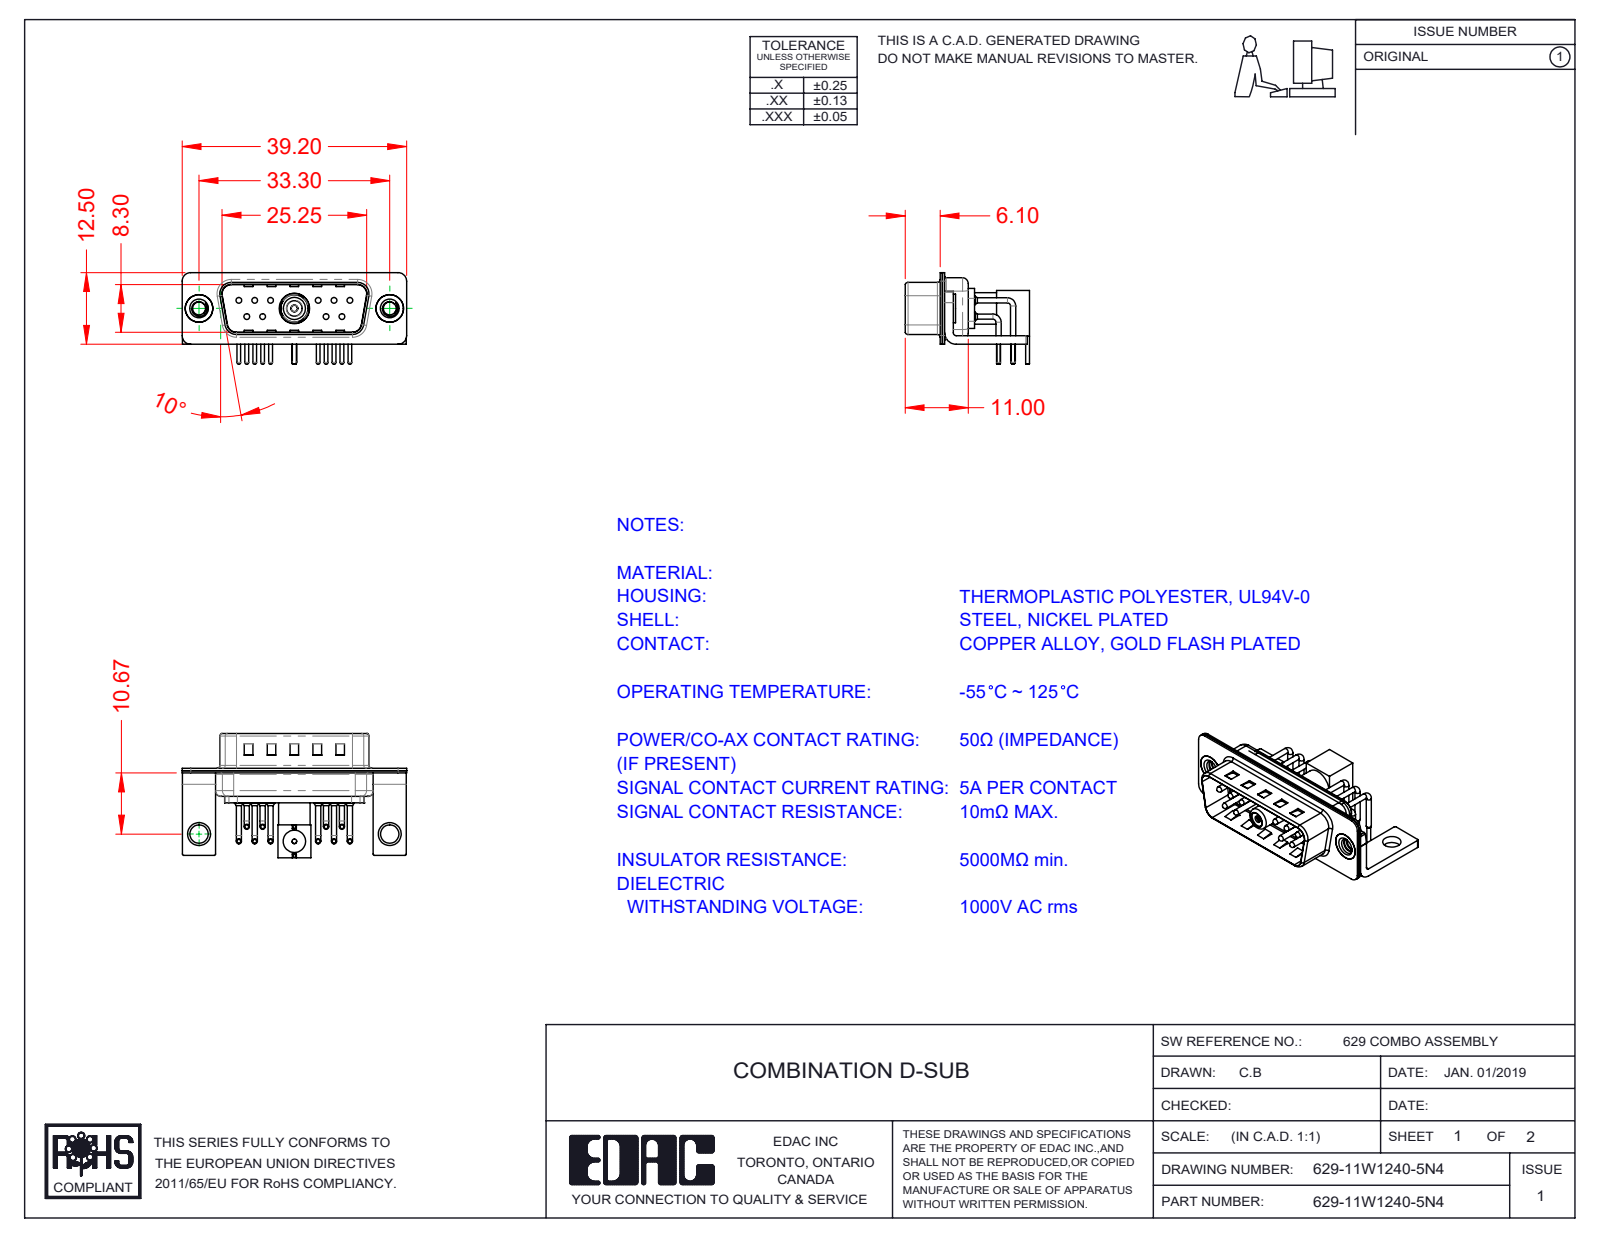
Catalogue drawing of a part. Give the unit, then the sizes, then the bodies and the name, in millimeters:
Units: millimetres
Overall size (bounding box): 39.2 × 21.71 × 16
Round holes (diameter × count): ⌀1.6 ×11, ⌀0.75 ×10, ⌀2 ×10, ⌀2.26 ×2, ⌀3.2 ×2, ⌀4 ×2, ⌀4.8 ×2, ⌀0.8 ×1, ⌀1.1 ×1, ⌀1.2 ×1, ⌀1.5 ×1, ⌀2.5 ×1
Round bosses / shafts (diameter × count): ⌀0.9 ×20, ⌀1.5 ×10, ⌀1 ×10, ⌀0.65 ×10, ⌀5 ×2, ⌀4.9 ×2, ⌀0.8 ×2, ⌀5.5 ×1
Partial cylindrical surfaces — rounded edges, fillets, slot ends (radius × count): R0.25 ×16, R1.5 ×16, R2 ×13, R1.01 ×10, R0.5 ×9, R1.6 ×8, R1 ×7, R0.6 ×4
Main face-to-face distances: 0.4, 0.8, 1.5, 9.5, 9.1, 9.9, 8.7, 0.6, 1.9, 0.35
Hole centre spacings: 3.16, 2.77, 13.85, 16.7, 11.08, 16.62, 5.03, 5.04
Volume: 2 479 mm³ · Surface area: 6 665 mm²
Bodies: 24 solids, 1645 faces (865 planar, 582 cylindrical, 198 other)
Part name (STEP PRODUCT): Insulator Socket; Insulator RA Pin; 629Combo Shell Front_15 Contacts; Co-Ax Jack_RA PC Tail (+8 more)
STEP written by: SolidWorks 2020 (CONFIG_CONTROL_DESIGN)
